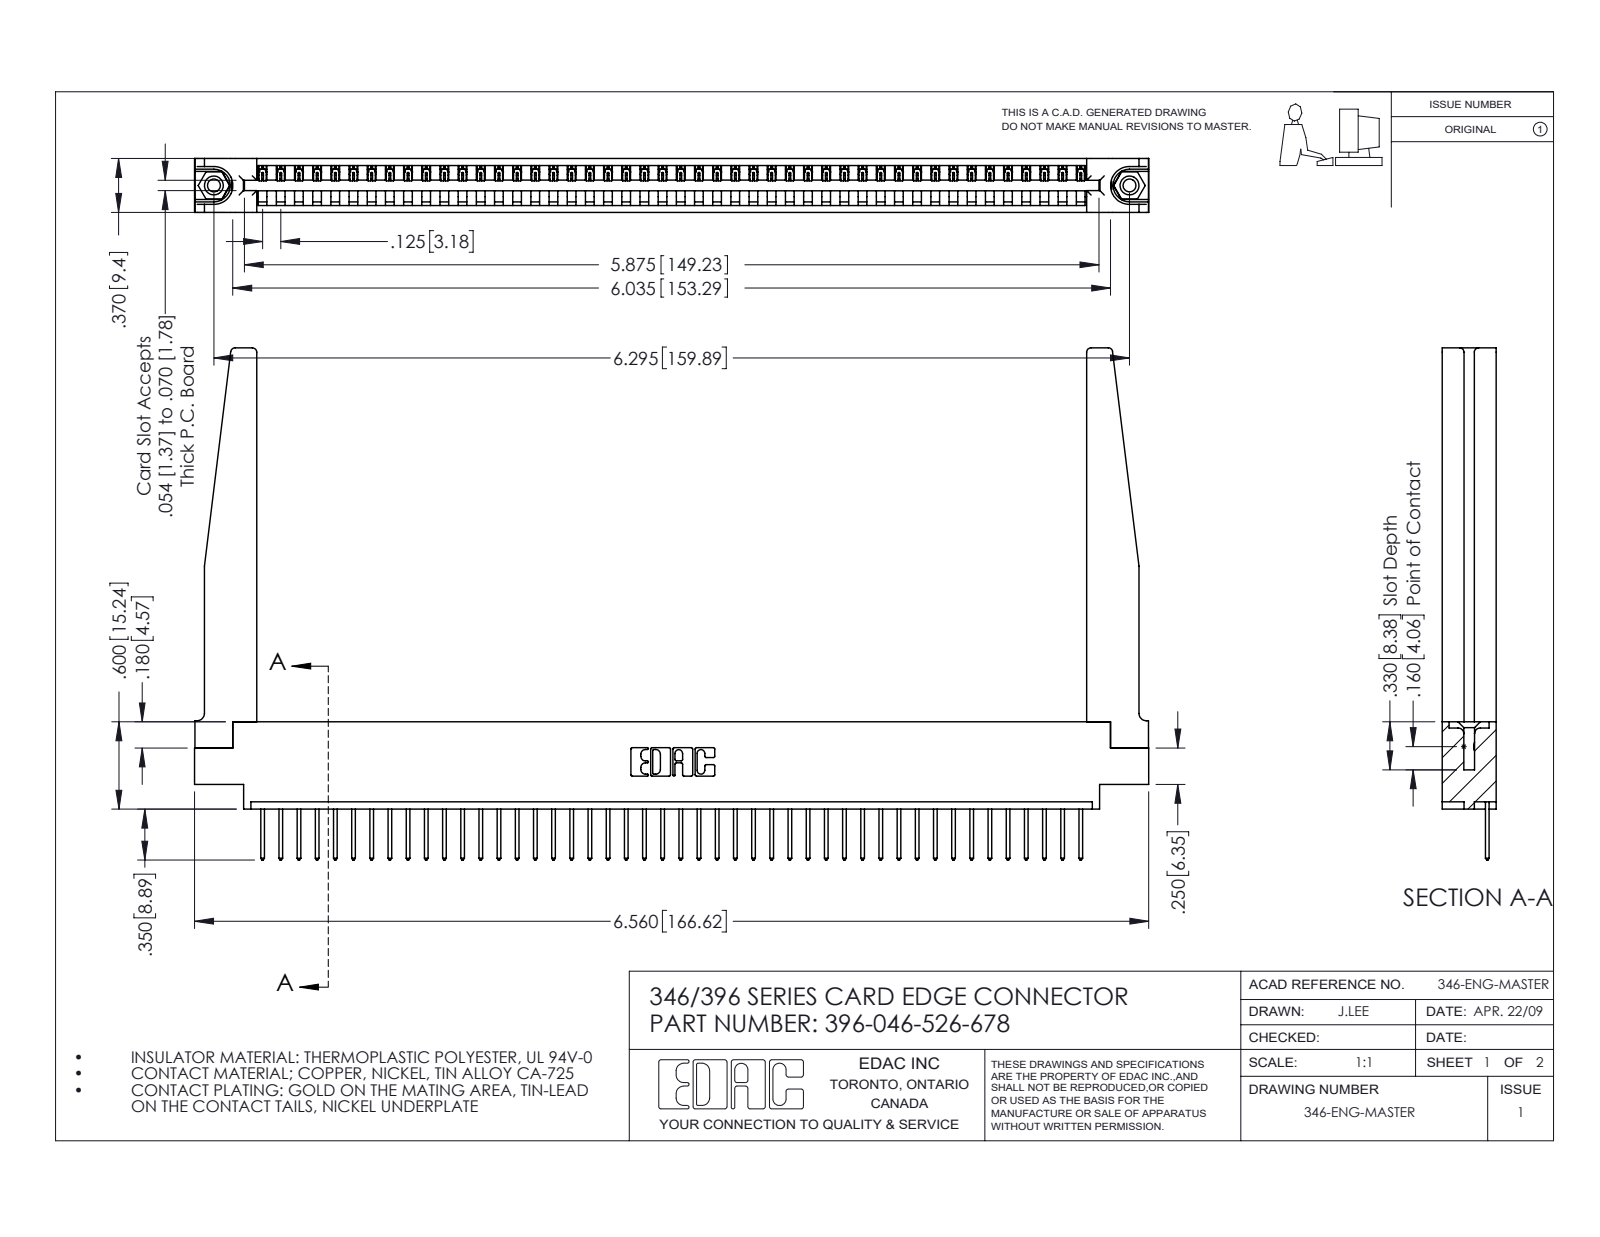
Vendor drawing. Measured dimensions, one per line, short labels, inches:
name: 345-292-001_345-293-126; 346 Part_0.170 Offset - 0.156 Dia-TH; 396-046-526-678; 346-220-078_345-220-078 (+1 more)
written by: SolidWorks 2016 (CONFIG_CONTROL_DESIGN)
unit: in
bodies: 51 solids, 3028 faces (2062 planar, 914 cylindrical, 52 other)
size: 6.56 × 3.52 × 0.37
volume: 1.385 in³; area: 40.97 in²
holes: 2× ⌀0.089, 2× ⌀0.125, 2× ⌀0.156, 1× ⌀0.064
bosses: 2× ⌀0.155
rounds: 92× R0.006, 92× R0.01, 22× R0.01, 8× R0.03, 6× R0.007, 6× R0.031, 3× R0.026, 2× R0.031
face distances: 0.37, 0.048, 0.322, 0.072, 0.148, 0.25, 0.15, 0.298, 0.025, 0.222
hole spacings: 0.246, 6.086, 6.295
